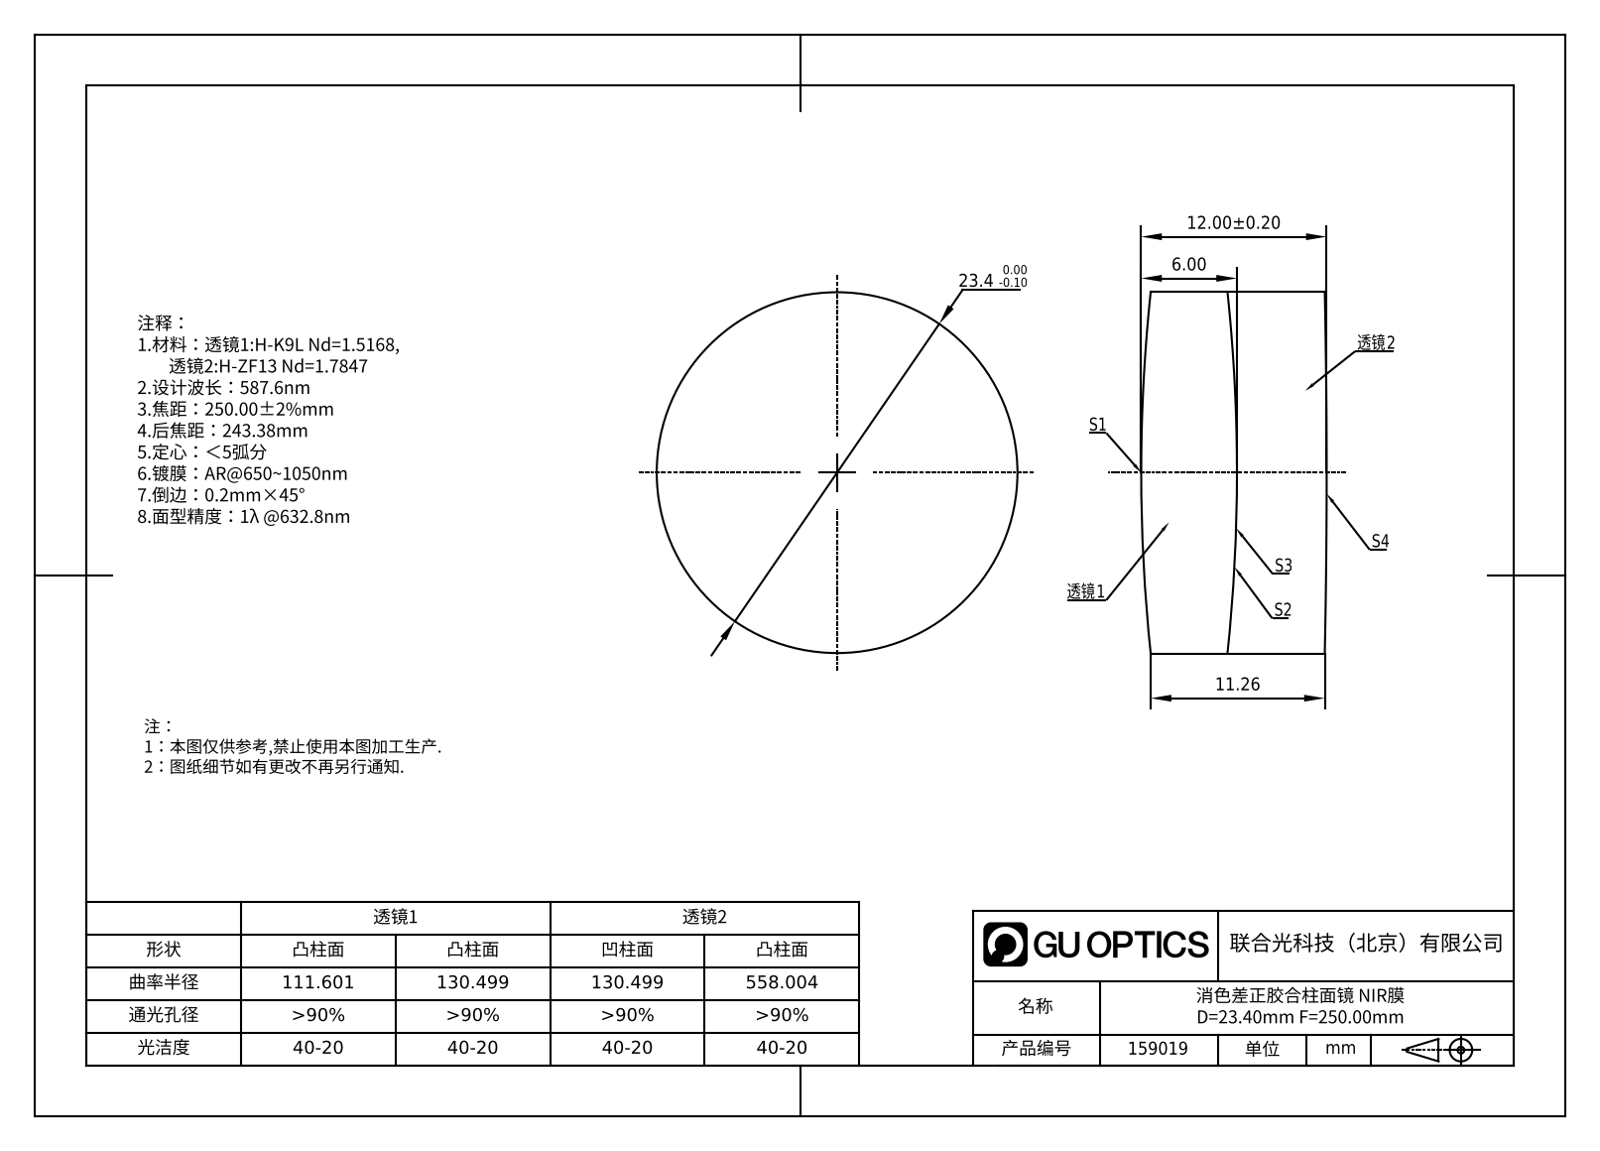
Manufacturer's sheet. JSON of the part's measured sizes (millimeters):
{"part_name": "159019", "step_written_by": "SolidWorks 2020 (CONFIG_CONTROL_DESIGN)", "units": "millimeters", "bodies": {"solids": 1, "faces": 5, "planar": 0, "cylindrical": 5, "other": 0}, "overall_size": [23.4, 23.4, 12], "volume_mm3": 5080, "surface_area_mm2": 1716, "round_bosses_or_shafts": [[23.4, 1]], "partial_cylinders_radius": [[111.6, 1], [558, 1]]}
